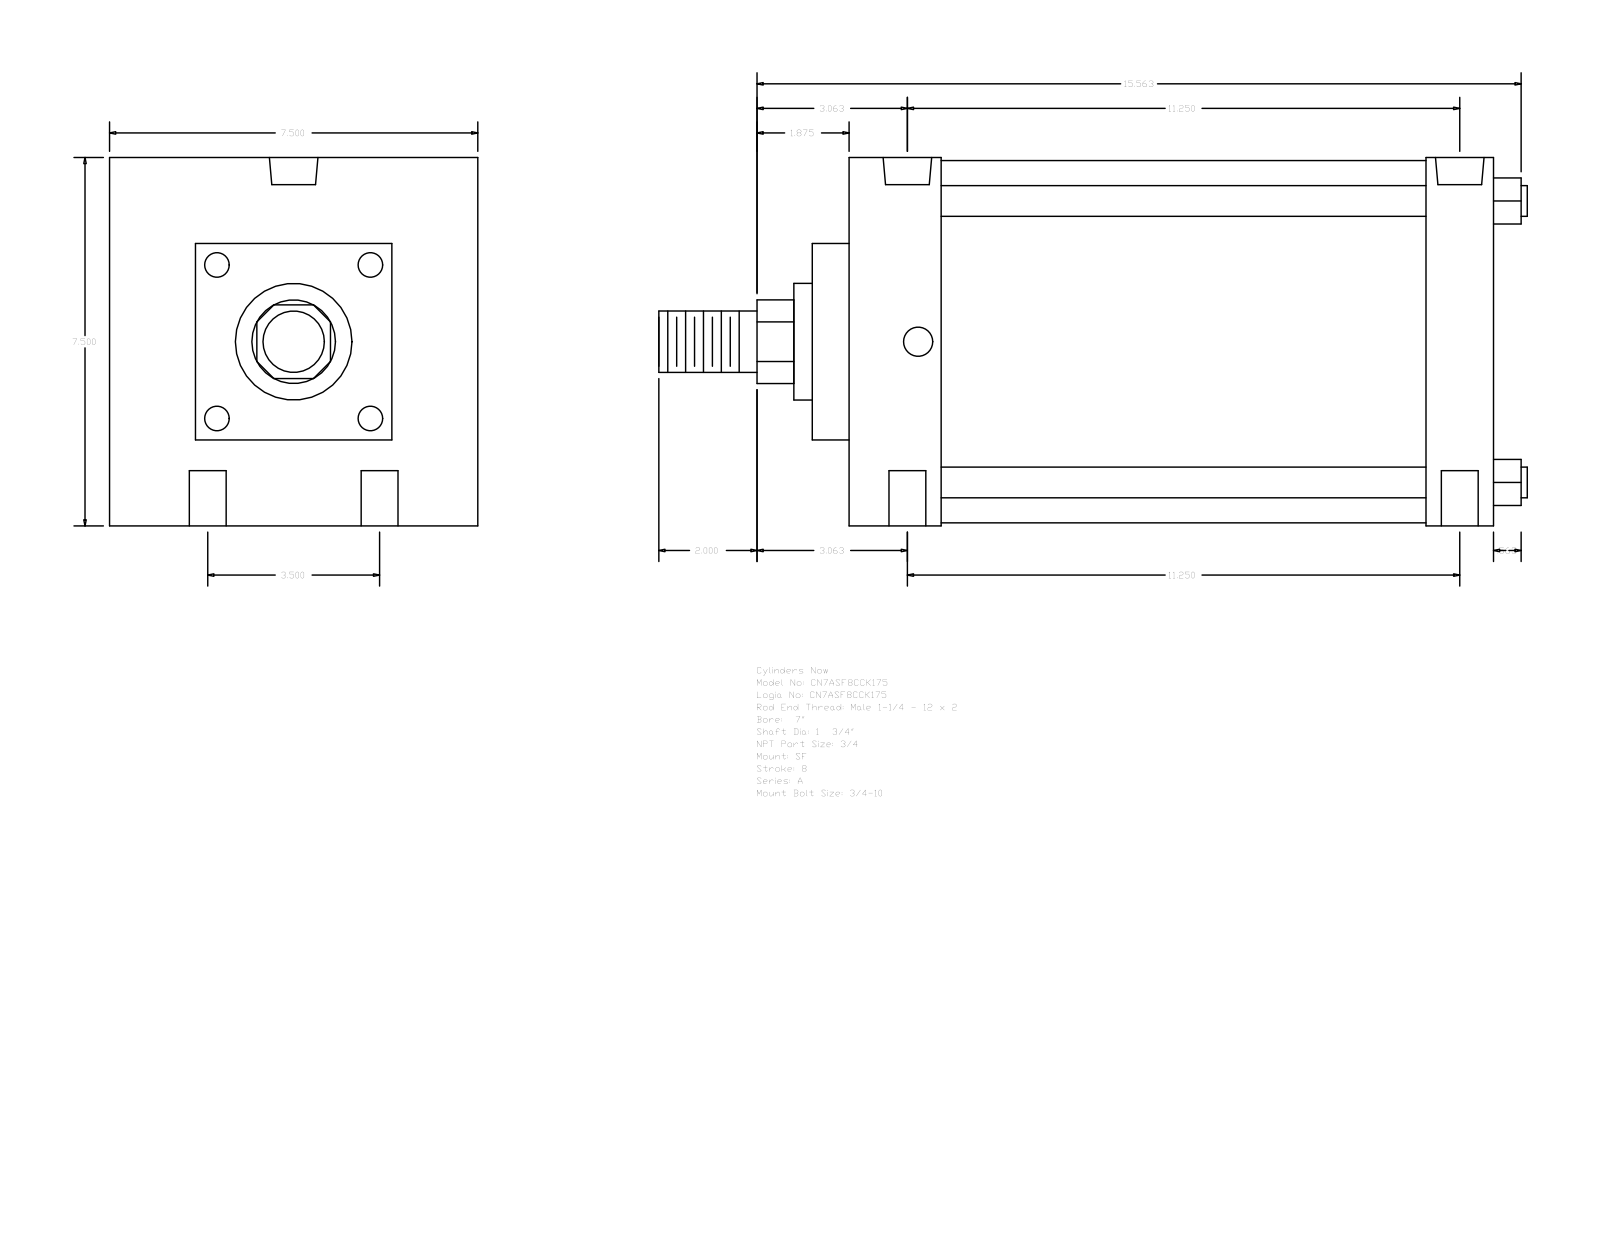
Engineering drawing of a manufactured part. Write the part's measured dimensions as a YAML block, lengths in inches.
part_name: "A_SF__0700_1.75"
step_written_by: "GSSL Pune (CONFIG_CONTROL_DESIGN)"
units: inches
bodies: {solids: 0, faces: 93, planar: 67, cylindrical: 26, other: 0}
overall_size: [17.687, 7.5, 7.5]
round_holes:
  - {diameter: 0.75, count: 4}
  - {diameter: 0.594, count: 2}
  - {diameter: 0.989, count: 2}
round_bosses_or_shafts:
  - {diameter: 0.625, count: 4}
  - {diameter: 7.375, count: 1}
  - {diameter: 2.375, count: 1}
  - {diameter: 1.75, count: 1}
  - {diameter: 1.25, count: 1}
partial_cylinders:
  - {radius: 0.852, count: 1}
face_to_face_distances: [7.5, 13.125, 5.75, 0.75, 1.875, 11.75, 9.875, 11.25, 1.375, 1.75]
hole_center_spacings: [1.75, 11.385, 11.25, 3.5, 11.782, 10.812]
